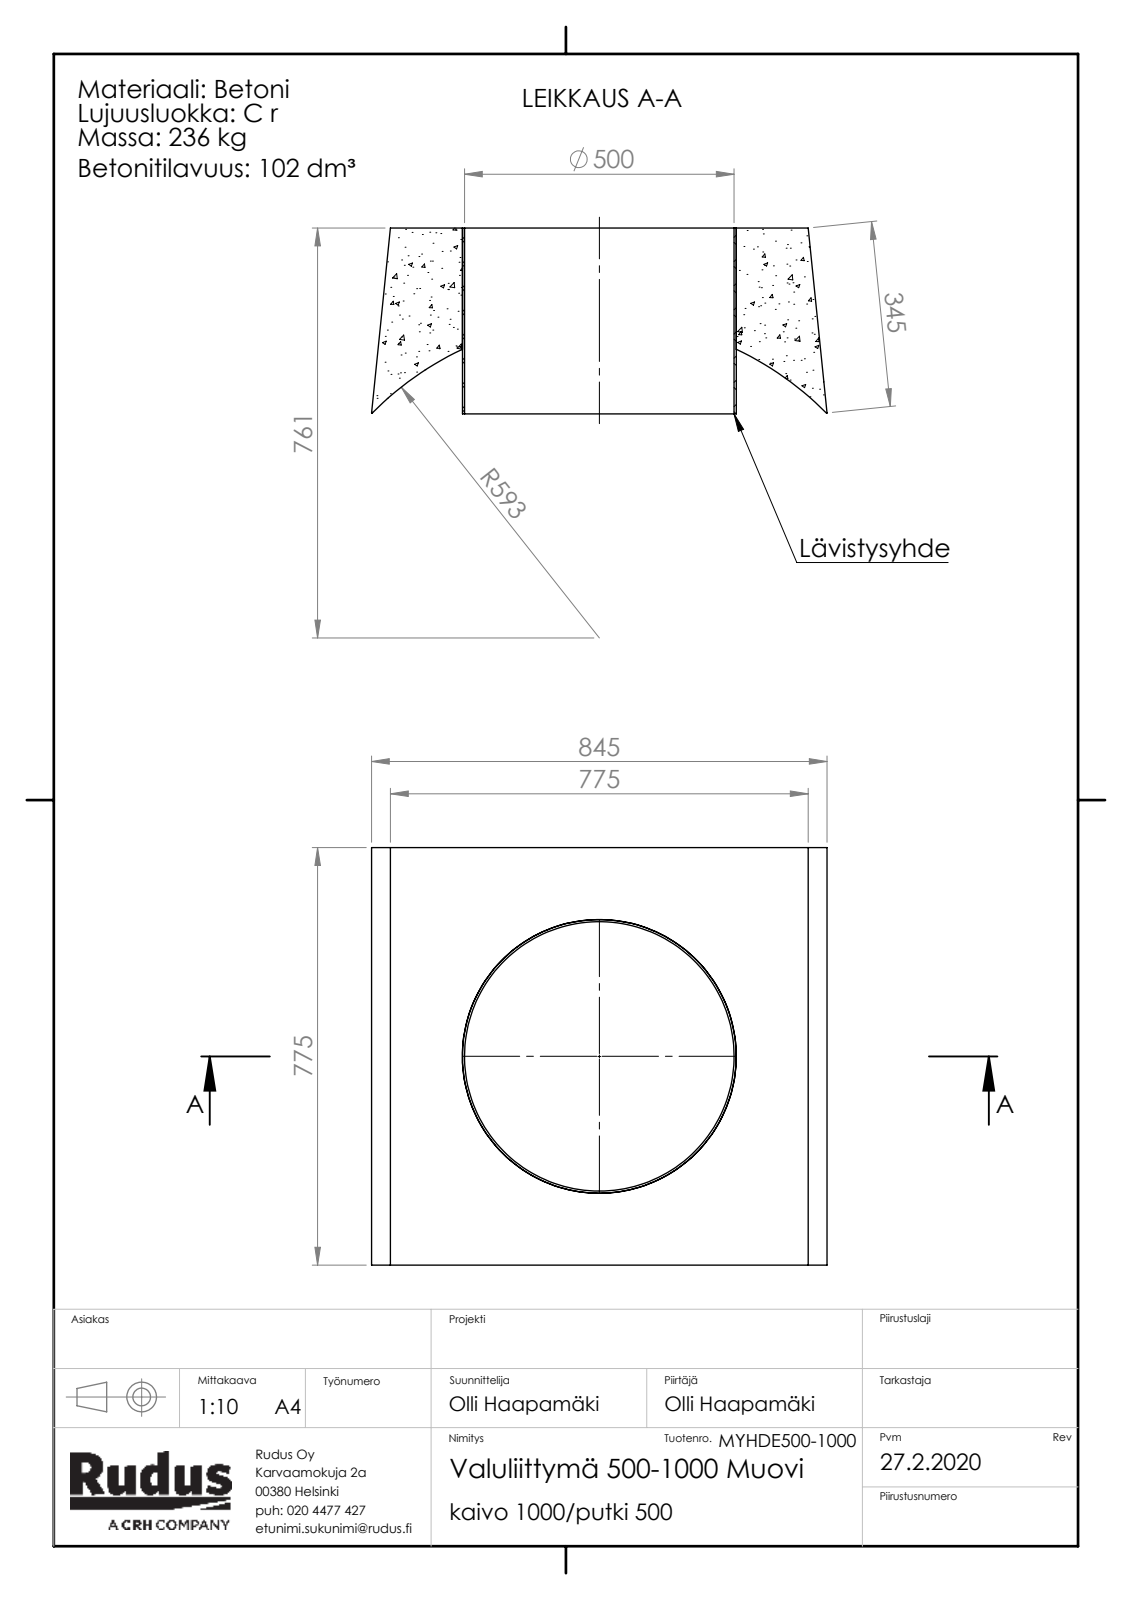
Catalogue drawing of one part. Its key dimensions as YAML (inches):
part_name: "muovi-lavistysyhde; kaivo-osa-valuliittyma-runko_muovi; Rudus MYHDE500-1000 Valuliittymä 500-1000 Muovi"
step_written_by: "SolidWorks 2019 (CONFIG_CONTROL_DESIGN)"
units: inches
bodies: {solids: 2, faces: 16, planar: 9, cylindrical: 7, other: 0}
overall_size: [33.268, 30.512, 13.583]
volume: 6218
surface_area: 4997
round_holes:
  - {diameter: 19.685, count: 1}
  - {diameter: 20, count: 1}
partial_cylinders:
  - {radius: 23.346, count: 1}
face_to_face_distances: [30.512, 13.583]
